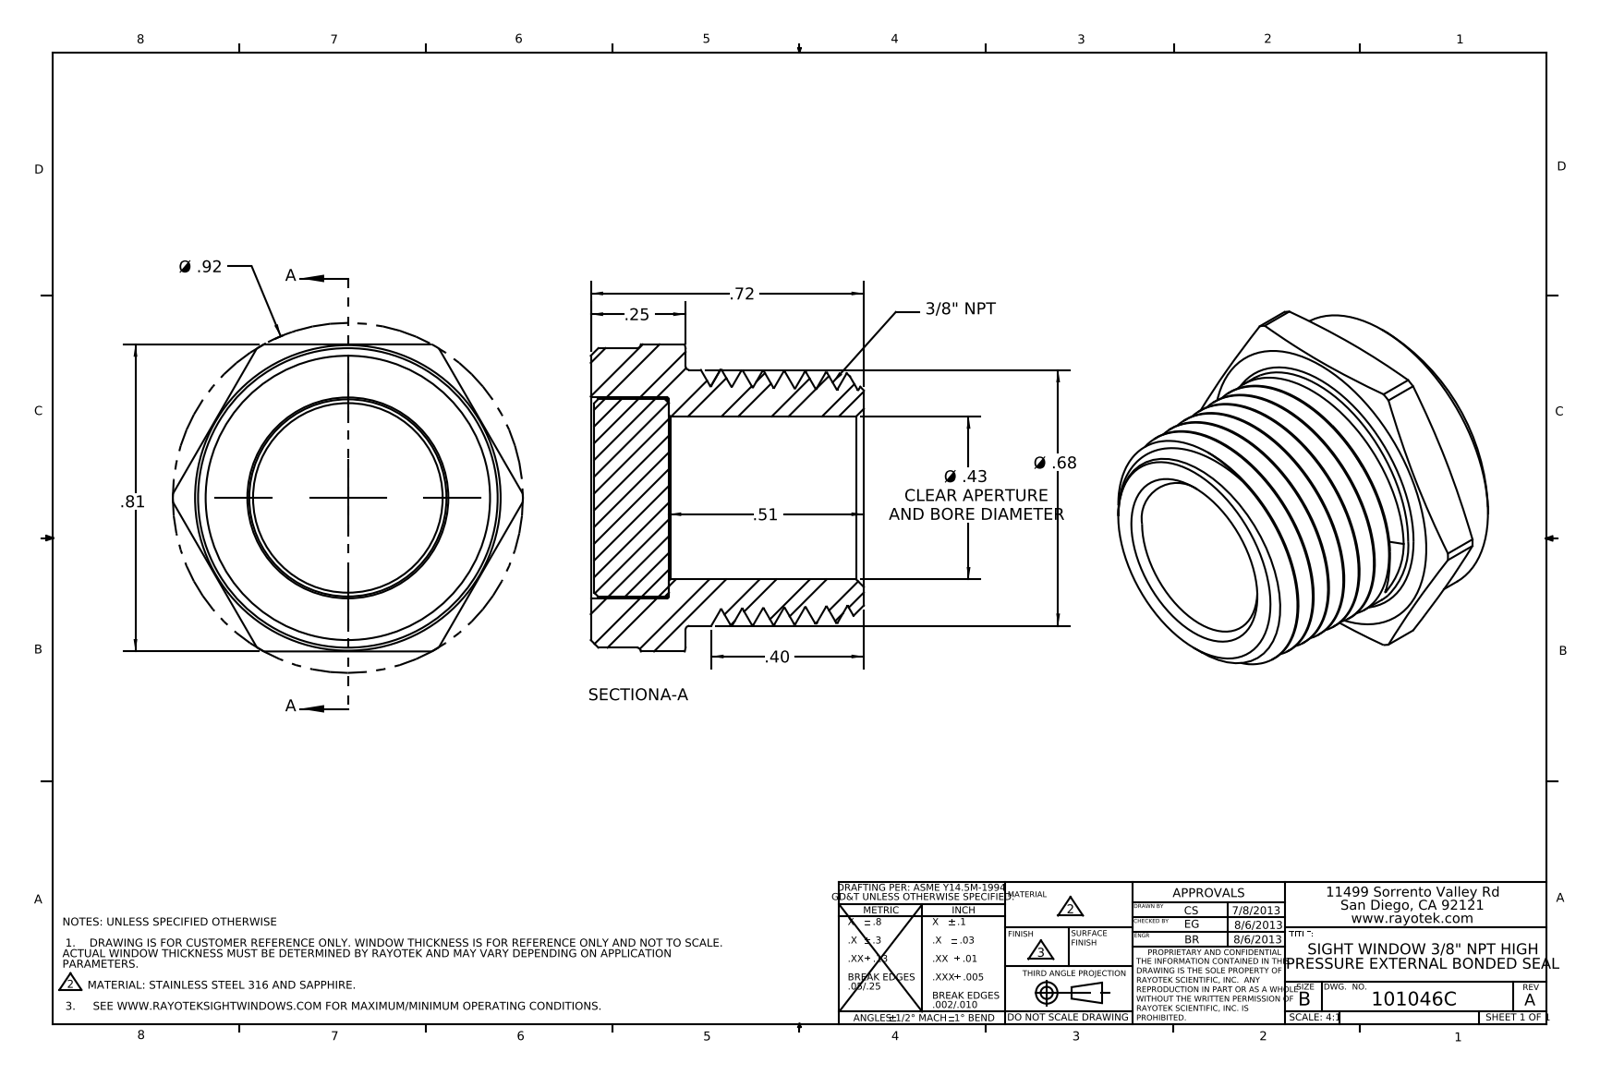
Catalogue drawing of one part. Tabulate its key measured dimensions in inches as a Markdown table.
| quantity | value |
| --- | --- |
| part name | 101046; 402046; 403046 |
| STEP written by | SolidWorks 2012 (AUTOMOTIVE_DESIGN) |
| units | inches |
| bodies | 2 solids, 72 faces (15 planar, 18 cylindrical, 39 other) |
| overall size | 0.923 × 0.81 × 0.72 |
| volume | 0.198 in³ |
| surface area | 4.707 in² |
| round holes (diameter × count) | 0.43 × 1, 0.53 × 1 |
| round bosses / shafts (diameter × count) | 0.79 × 1, 0.675 × 1, 0.52 × 1 |
| partial cylindrical surfaces (radius × count) | 0.462 × 1 |
| main face-to-face distances | 0.206, 0.197, 0.81, 0.25, 0.241, 0.044, 0.72, 0.711, 0.514, 0.47 |
